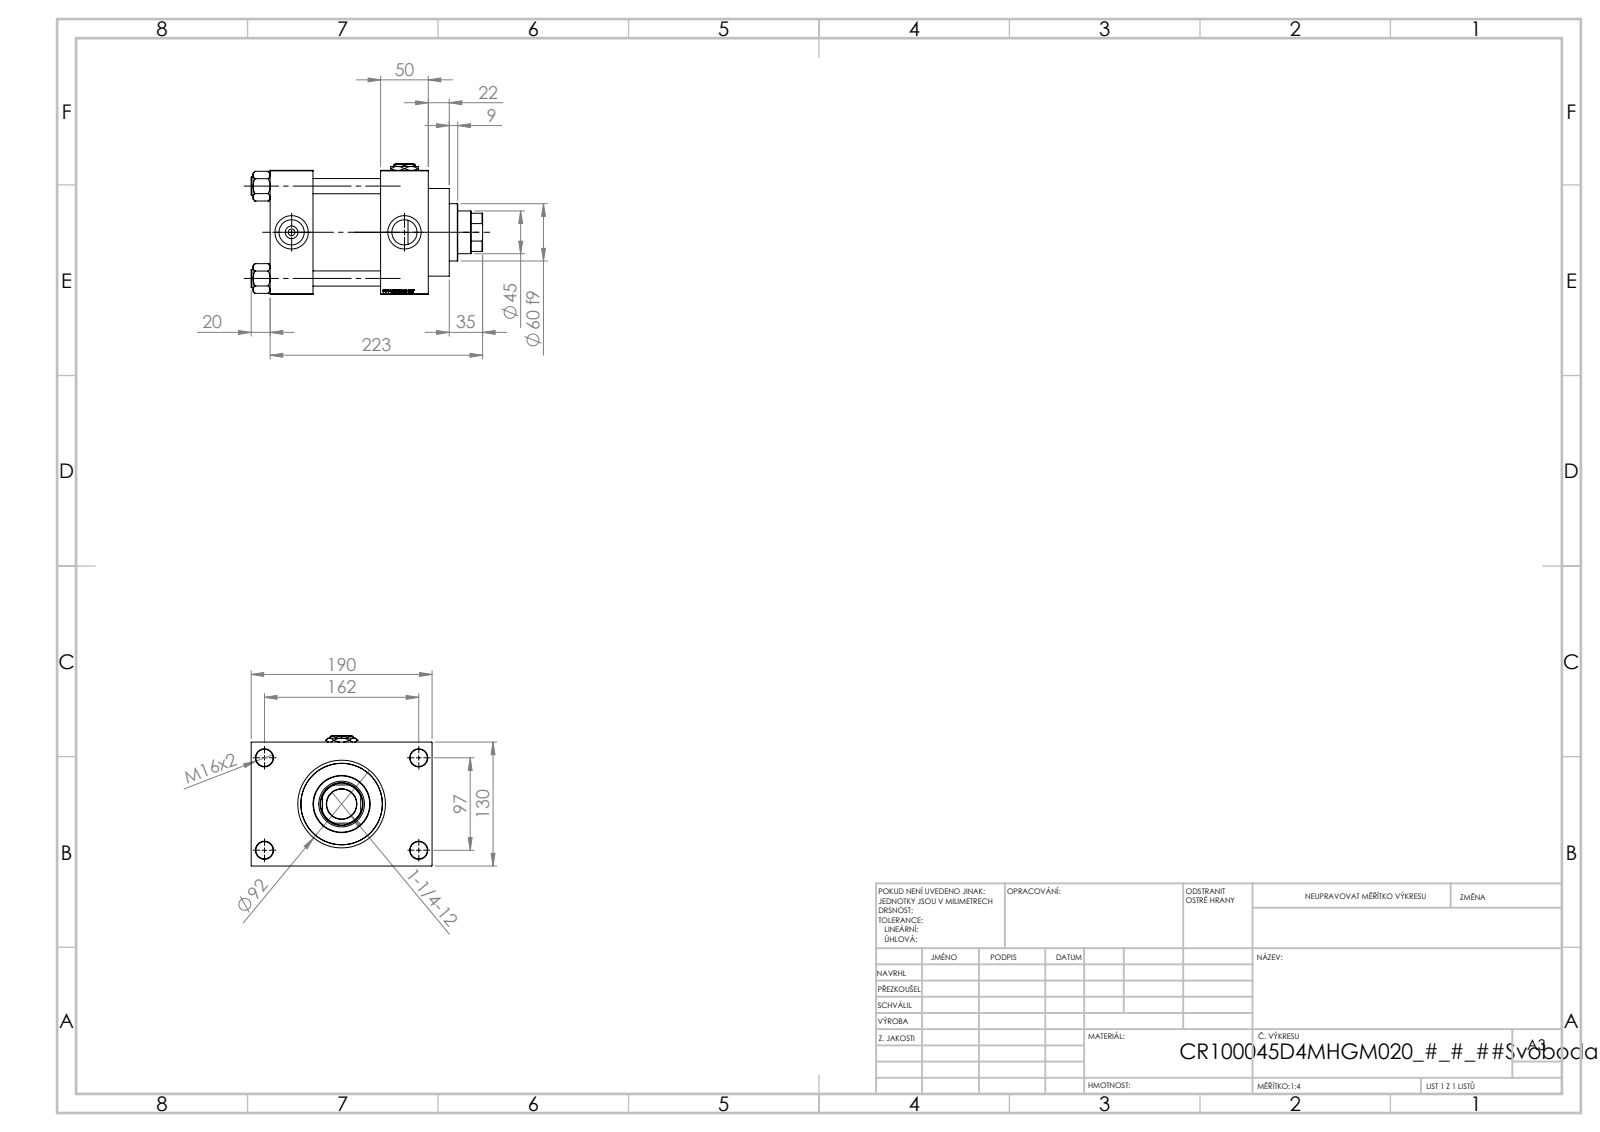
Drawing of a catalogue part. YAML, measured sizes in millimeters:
part_name: "NUT_M5_D; Zatka_pro_OIL_PORT; V215CR_D_TYCINKA; V215CR_VCP_D (+2 more)"
step_written_by: "SolidWorks 2019 (CONFIG_CONTROL_DESIGN)"
units: millimeters
bodies: {solids: 12, faces: 1199, planar: 569, cylindrical: 92, other: 538}
overall_size: [243, 190, 137]
volume: 2580000
surface_area: 357844
round_holes:
  - {diameter: 16, count: 4}
  - {diameter: 18, count: 4}
  - {diameter: 26.44, count: 3}
  - {diameter: 35, count: 3}
  - {diameter: 7, count: 2}
  - {diameter: 31.5, count: 1}
  - {diameter: 45, count: 1}
  - {diameter: 48, count: 1}
  - {diameter: 76, count: 1}
  - {diameter: 85.5, count: 1}
  - {diameter: 100, count: 1}
round_bosses_or_shafts:
  - {diameter: 19, count: 4}
  - {diameter: 106, count: 1}
  - {diameter: 92, count: 1}
  - {diameter: 60, count: 1}
partial_cylinders:
  - {radius: 22, count: 1}
face_to_face_distances: [130, 45, 116, 71, 166, 121, 50, 30, 160, 20]
hole_center_spacings: [32.55, 68.52, 94.41, 96.9, 102.27, 129.45, 161.73, 97]
